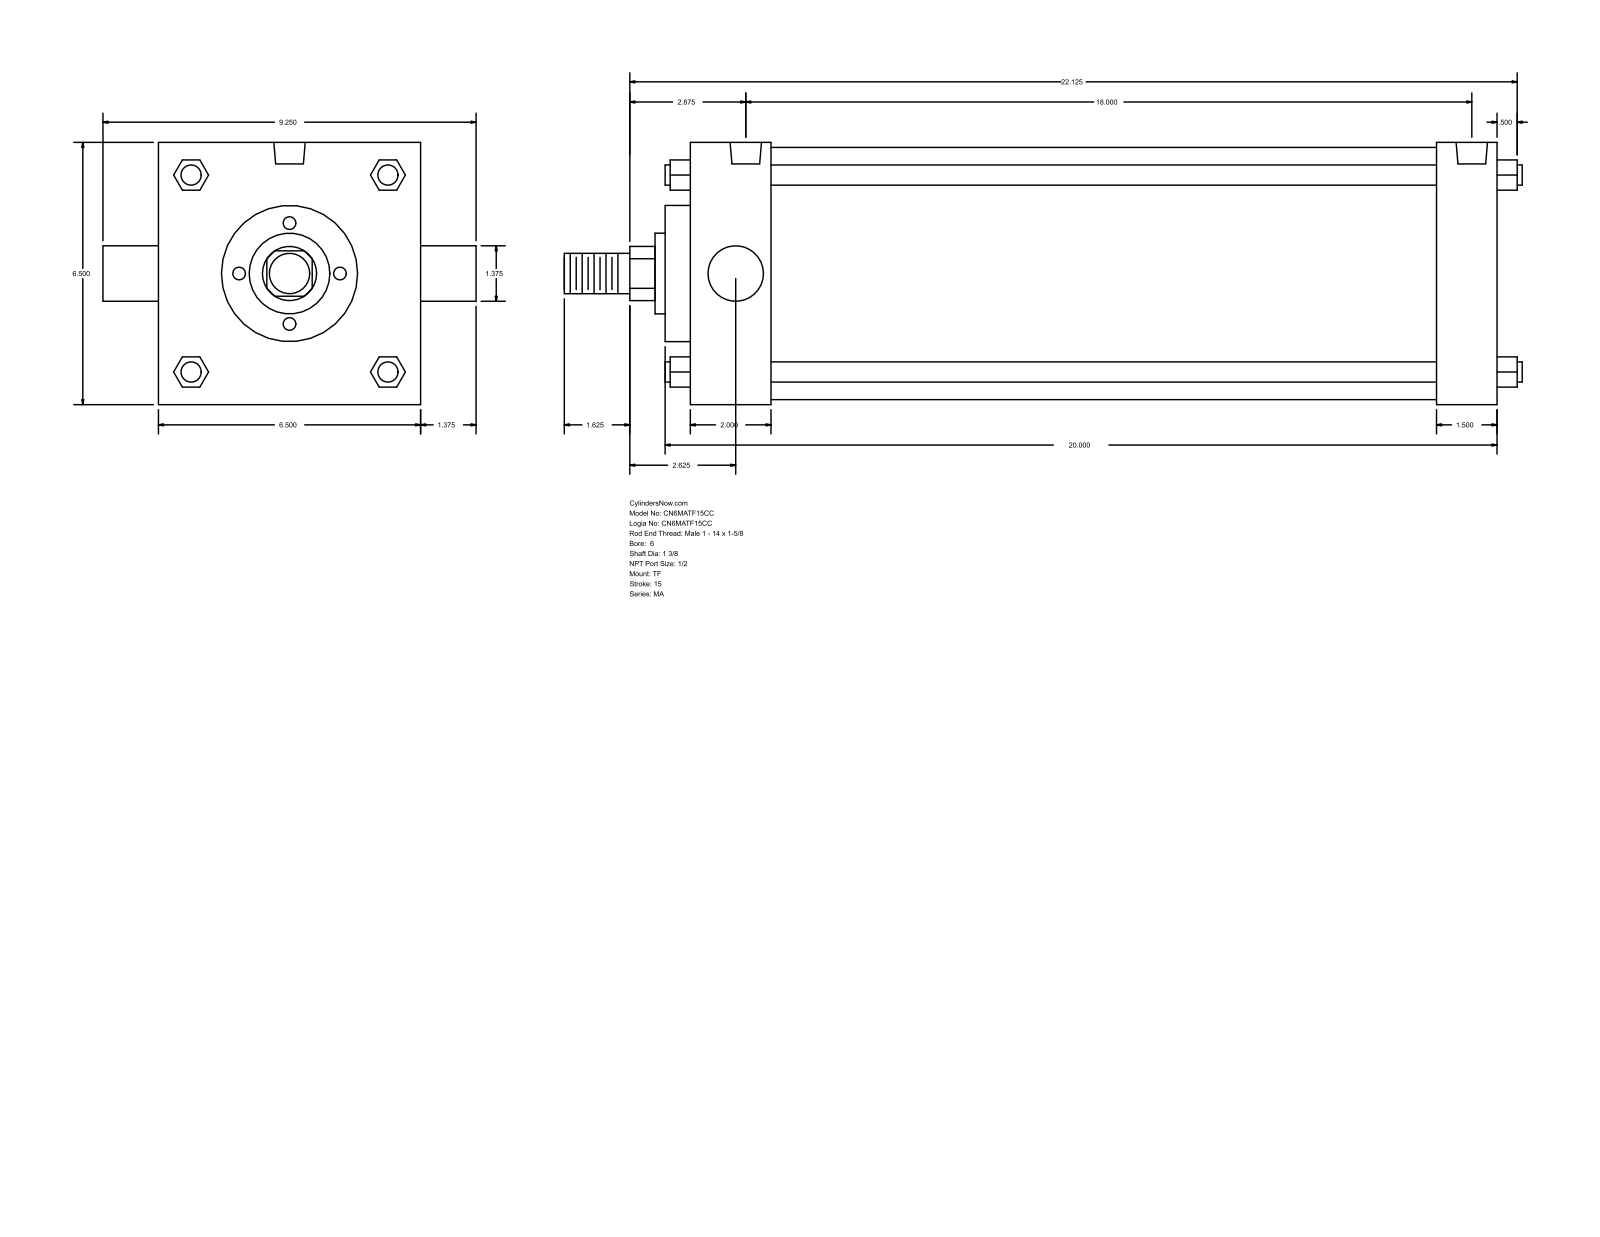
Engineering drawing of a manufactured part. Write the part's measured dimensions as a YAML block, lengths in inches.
part_name: "MA_TF__0600_1.375"
step_written_by: "GSSL Pune (CONFIG_CONTROL_DESIGN)"
units: inches
bodies: {solids: 0, faces: 122, planar: 93, cylindrical: 29, other: 0}
overall_size: [23.75, 9.25, 6.5]
round_holes:
  - {diameter: 0.687, count: 3}
  - {diameter: 0.778, count: 2}
round_bosses_or_shafts:
  - {diameter: 0.5, count: 4}
  - {diameter: 1.375, count: 2}
  - {diameter: 6.25, count: 1}
  - {diameter: 3.375, count: 1}
  - {diameter: 2, count: 1}
  - {diameter: 1, count: 1}
partial_cylinders:
  - {radius: 0.672, count: 1}
face_to_face_distances: [6.5, 20.125, 2, 18.625, 18.125, 16.625, 1.5, 2.625, 0.625, 19.25]
hole_center_spacings: [0.125, 18, 18.125]
